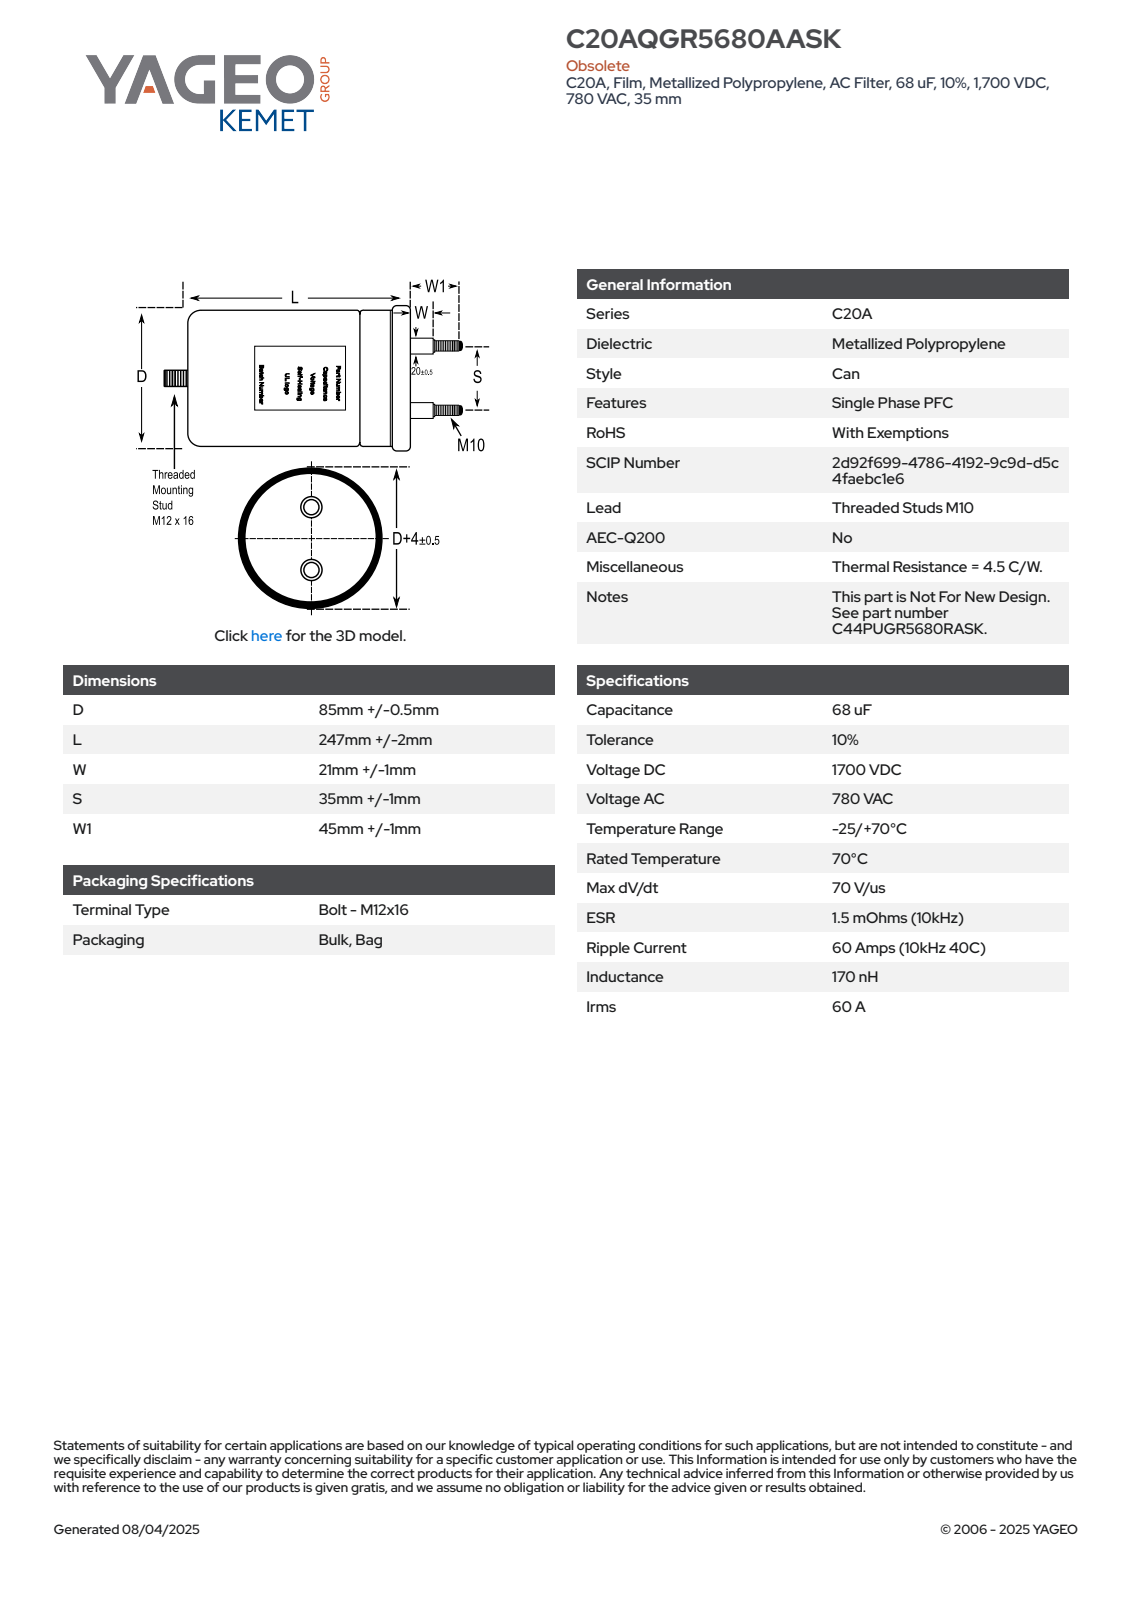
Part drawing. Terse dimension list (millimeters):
name: CFP_C44P_85X247_D85.5L249S35
written by: SolidWorks 2014 (AUTOMOTIVE_DESIGN)
unit: mm
bodies: 1 solid, 105 faces (32 planar, 36 cylindrical, 37 other)
size: 311 × 90 × 90
volume: 1 453 000 mm³; area: 83 783 mm²
bosses: 3× ⌀12, 2× ⌀20.5, 2× ⌀10, 1× ⌀90, 1× ⌀85.5
rounds: 1× R42.76
face distances: 249, 270, 21, 241.01, 7.99, 28.99, 295, 53.99, 46, 25
